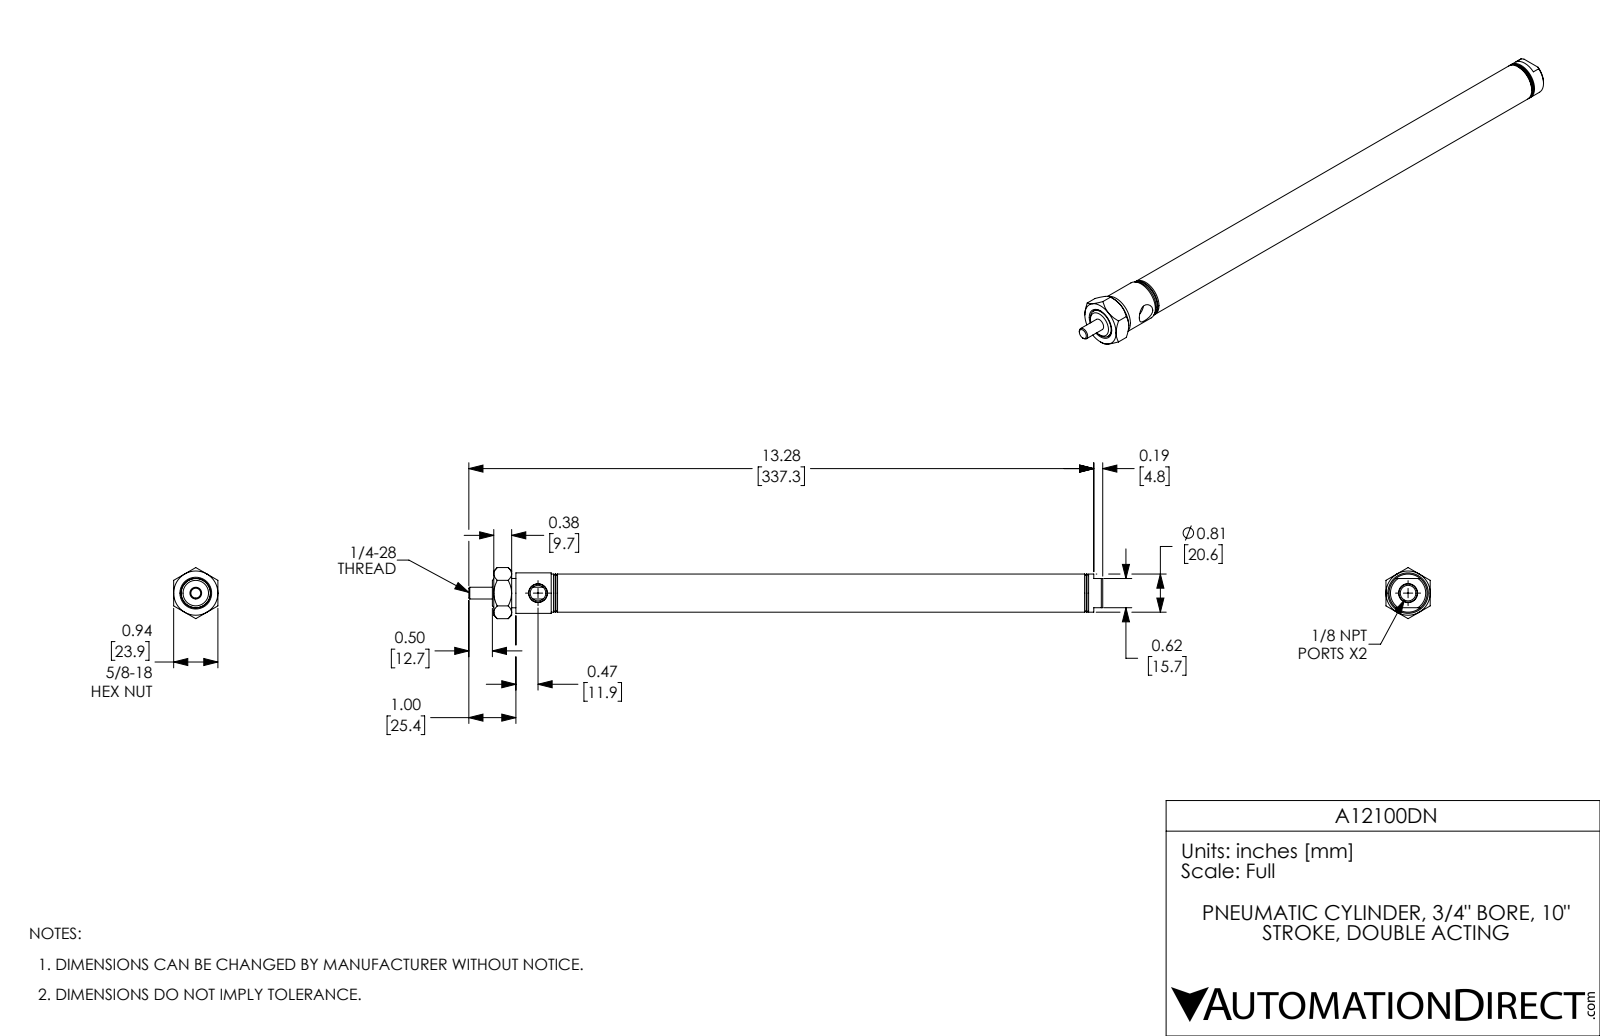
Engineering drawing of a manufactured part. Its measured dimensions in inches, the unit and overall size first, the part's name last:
Units: inches
Overall size (bounding box): 13.47 × 1.085 × 0.94
Round holes (diameter × count): ⌀0.332 ×2, ⌀0.25 ×1, ⌀0.625 ×1, ⌀0.75 ×1
Round bosses / shafts (diameter × count): ⌀0.86 ×1, ⌀0.81 ×1, ⌀0.623 ×1
Main face-to-face distances: 11.485, 0.94, 0.5, 0.985, 1.485, 10.5, 10, 11.575, 11.075, 1.075
Volume: 2.739 in³ · Surface area: 76.38 in²
Bodies: 3 solids, 94 faces (27 planar, 28 cylindrical, 39 other)
Part name (STEP PRODUCT): A12100DN; A12100DN_Mounting Nut_D-9; A12100DN-Rod; A12100DN-MainBody
STEP written by: SolidWorks 2017 (AUTOMOTIVE_DESIGN)
